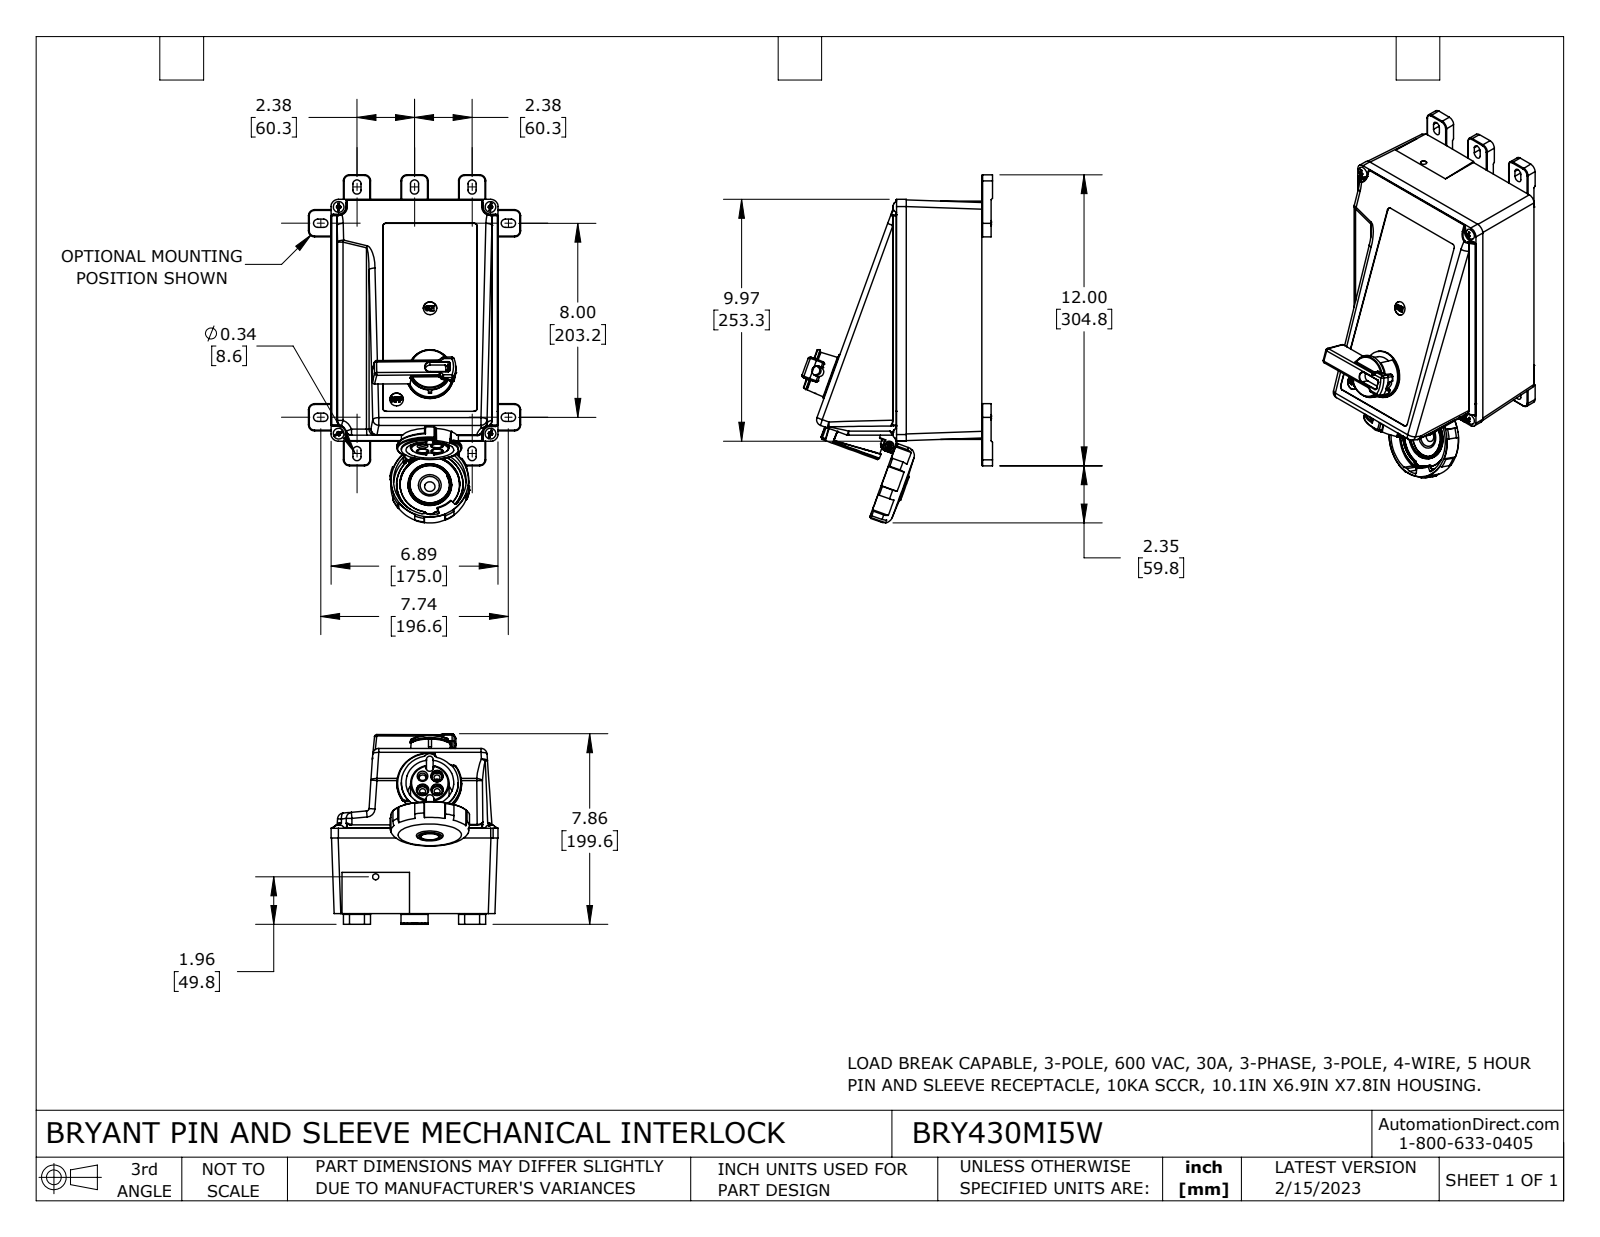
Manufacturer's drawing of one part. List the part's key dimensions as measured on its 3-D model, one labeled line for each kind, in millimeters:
Part name (STEP PRODUCT): BRY430MI5W
STEP written by: SolidWorks 2021 (CONFIG_CONTROL_DESIGN)
Units: millimetres
Bodies: 10 solids, 2065 faces (740 planar, 671 cylindrical, 654 other)
Overall size (bounding box): 364.6 × 199.6 × 175
Volume: 5 488 000 mm³ · Surface area: 300 000 mm²
Round holes (diameter × count): ⌀7.1 ×5, ⌀2 ×4, ⌀6.3 ×3, ⌀4 ×2, ⌀14.2 ×2, ⌀2.6 ×1, ⌀3.5 ×1, ⌀4 ×1, ⌀6.4 ×1, ⌀6.9 ×1, ⌀8.3 ×1, ⌀16.8 ×1
Round bosses / shafts (diameter × count): ⌀6.7 ×2, ⌀3.1 ×2, ⌀69.6 ×1, ⌀59.7 ×1, ⌀48.8 ×1, ⌀45.6 ×1, ⌀40.3 ×1, ⌀31.6 ×1
Partial cylindrical surfaces — rounded edges, fillets, slot ends (radius × count): R0.4 ×124, R0.8 ×54, R2 ×30, R6.4 ×24, R2.3 ×17, R0.3 ×16, R1.9 ×12, R4.3 ×10
Main face-to-face distances: 3, 245.2, 120.7, 249.7, 4.4, 105.9, 105.6, 3.8, 9.7, 0.9
Hole centre spacings: 17.8, 10.7, 15.2, 12.1, 25.8, 10.7, 10.8, 17.8
